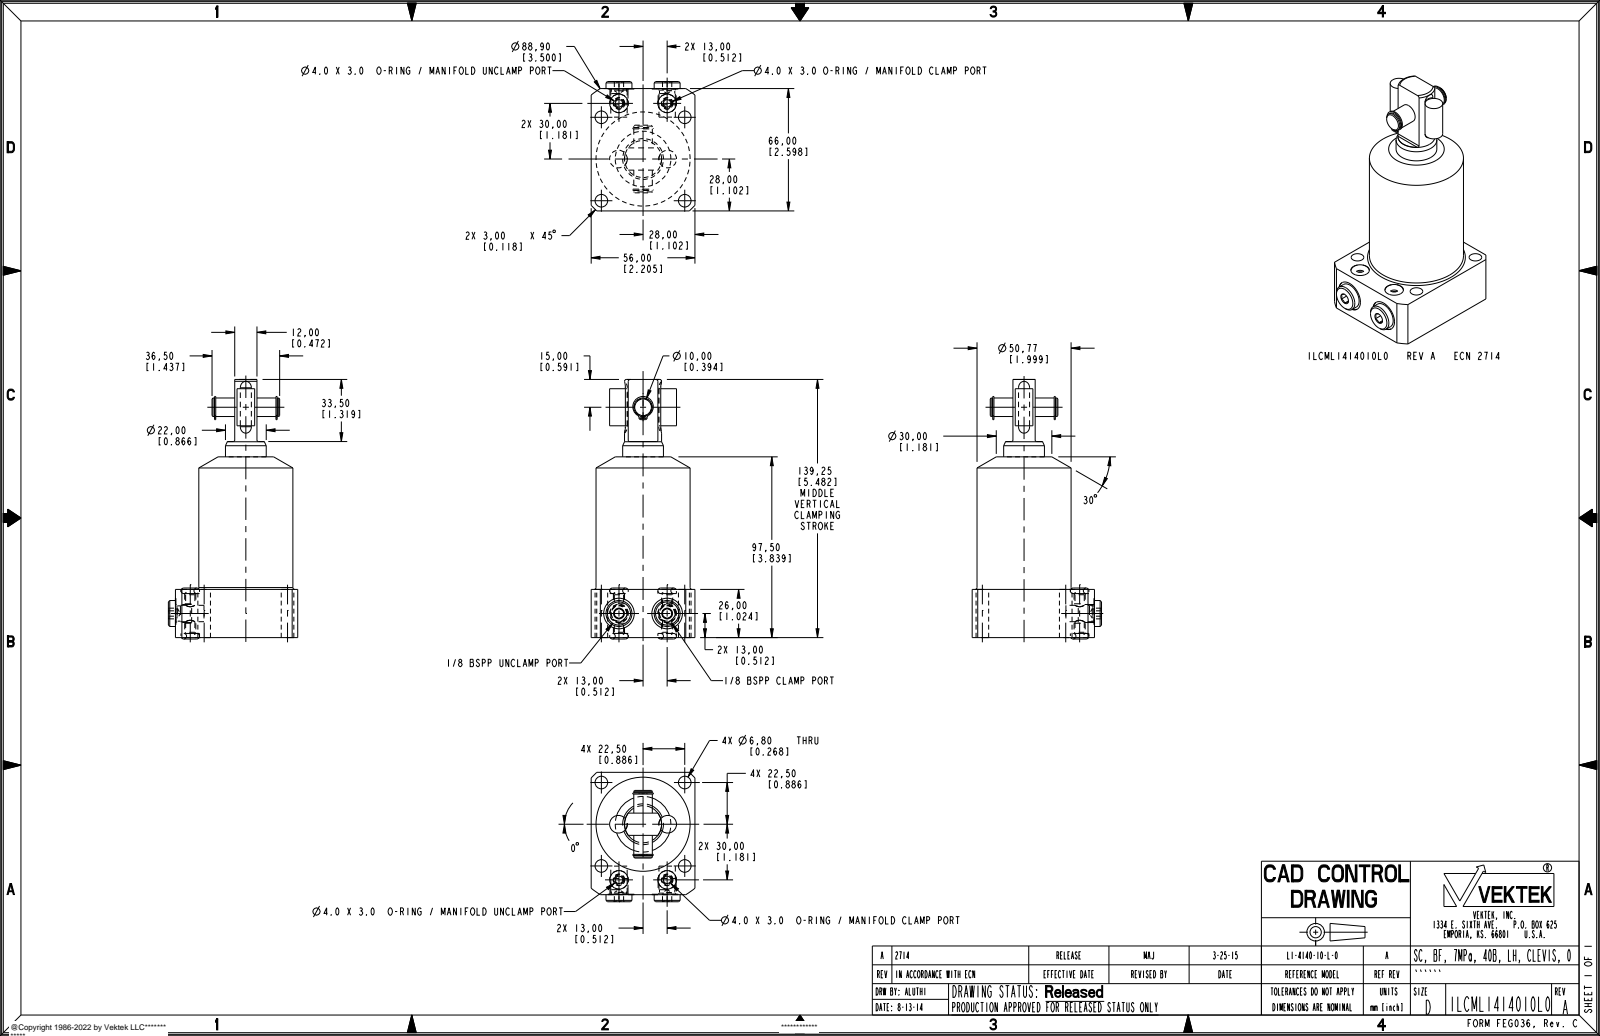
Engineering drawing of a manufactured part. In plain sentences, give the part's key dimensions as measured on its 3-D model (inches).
The part is named "ILCML1414010L0". Its 3-D file was written by "PRO/ENGINEER BY PARAMETRIC TECHNOLOGY CORPORATION, 2013320 (AUTOMOTIVE_DESIGN)". It is 7 solids with 234 faces: 80 planar, 98 cylindrical and 56 other. Overall it measures 5.512 by 2.748 by 2.205 inches. Its volume is 15 cubic inches and its surface area 54.16 square inches. Round holes: 4 of diameter 0.268, 2 of diameter 0.041, 2 of diameter 0.197, 2 of diameter 0.348, 2 of diameter 0.394, 2 of diameter 0.65. Round bosses or shafts: 2 of diameter 0.551, 2 of diameter 0.383, 2 of diameter 0.375, 2 of diameter 0.325, 2 of diameter 0.236, 1 of diameter 1.999, 1 of diameter 0.866, 1 of diameter 0.787. Partial cylindrical surfaces (rounded edges, fillets, slot ends): 2 of radius 0.031, 2 of radius 0.041, 2 of radius 0.058, 2 of radius 0.187, 1 of radius 1.75. The main face-to-face distances are 2.205, 1.024, 2.598, 0.866, 1.732, 1.339, 0.472, 1.26, 3.839, 2.815. The hole center spacings are 1.772, 0.476, 1.024, 1.428, 2.1, 2.495, 2.506, 4.183.
